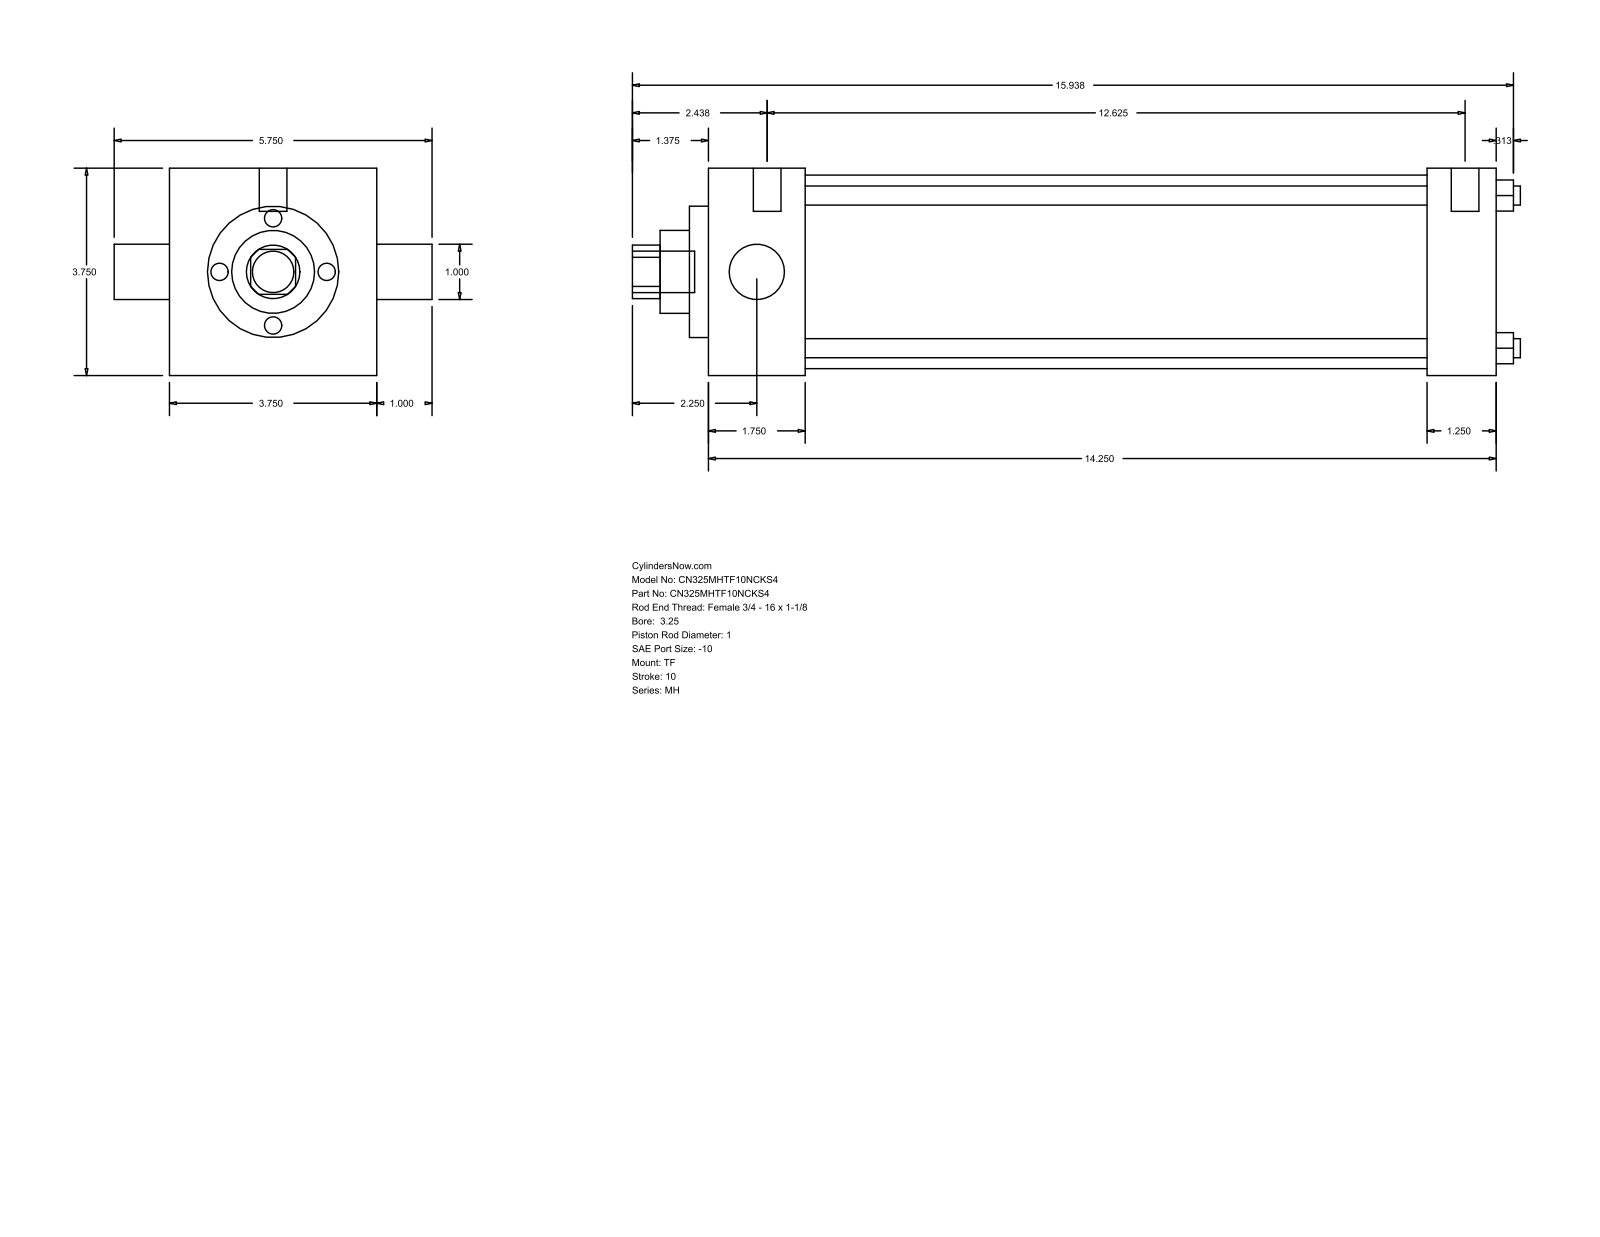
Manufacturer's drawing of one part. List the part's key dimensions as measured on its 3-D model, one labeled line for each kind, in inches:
Part name (STEP PRODUCT): MH_TF__0325_1
STEP written by: GSSL Pune (CONFIG_CONTROL_DESIGN)
Units: inches
Bodies: 0 solids, 86 faces (61 planar, 25 cylindrical, 0 other)
Overall size (bounding box): 16.063 × 5.75 × 3.75
Round holes (diameter × count): ⌀0.345 ×4, ⌀1 ×2, ⌀1.5 ×1, ⌀2.375 ×1, ⌀3.5 ×1
Round bosses / shafts (diameter × count): ⌀0.219 ×3, ⌀0.5 ×2, ⌀0.75 ×1
Partial cylindrical surfaces — rounded edges, fillets, slot ends (radius × count): R0.484 ×1
Main face-to-face distances: 3.75, 14.25, 1.75, 13, 11.25, 12.5, 1.25, 0.344, 2.094, 13.344
Hole centre spacings: 1.952, 2.76, 3.903
